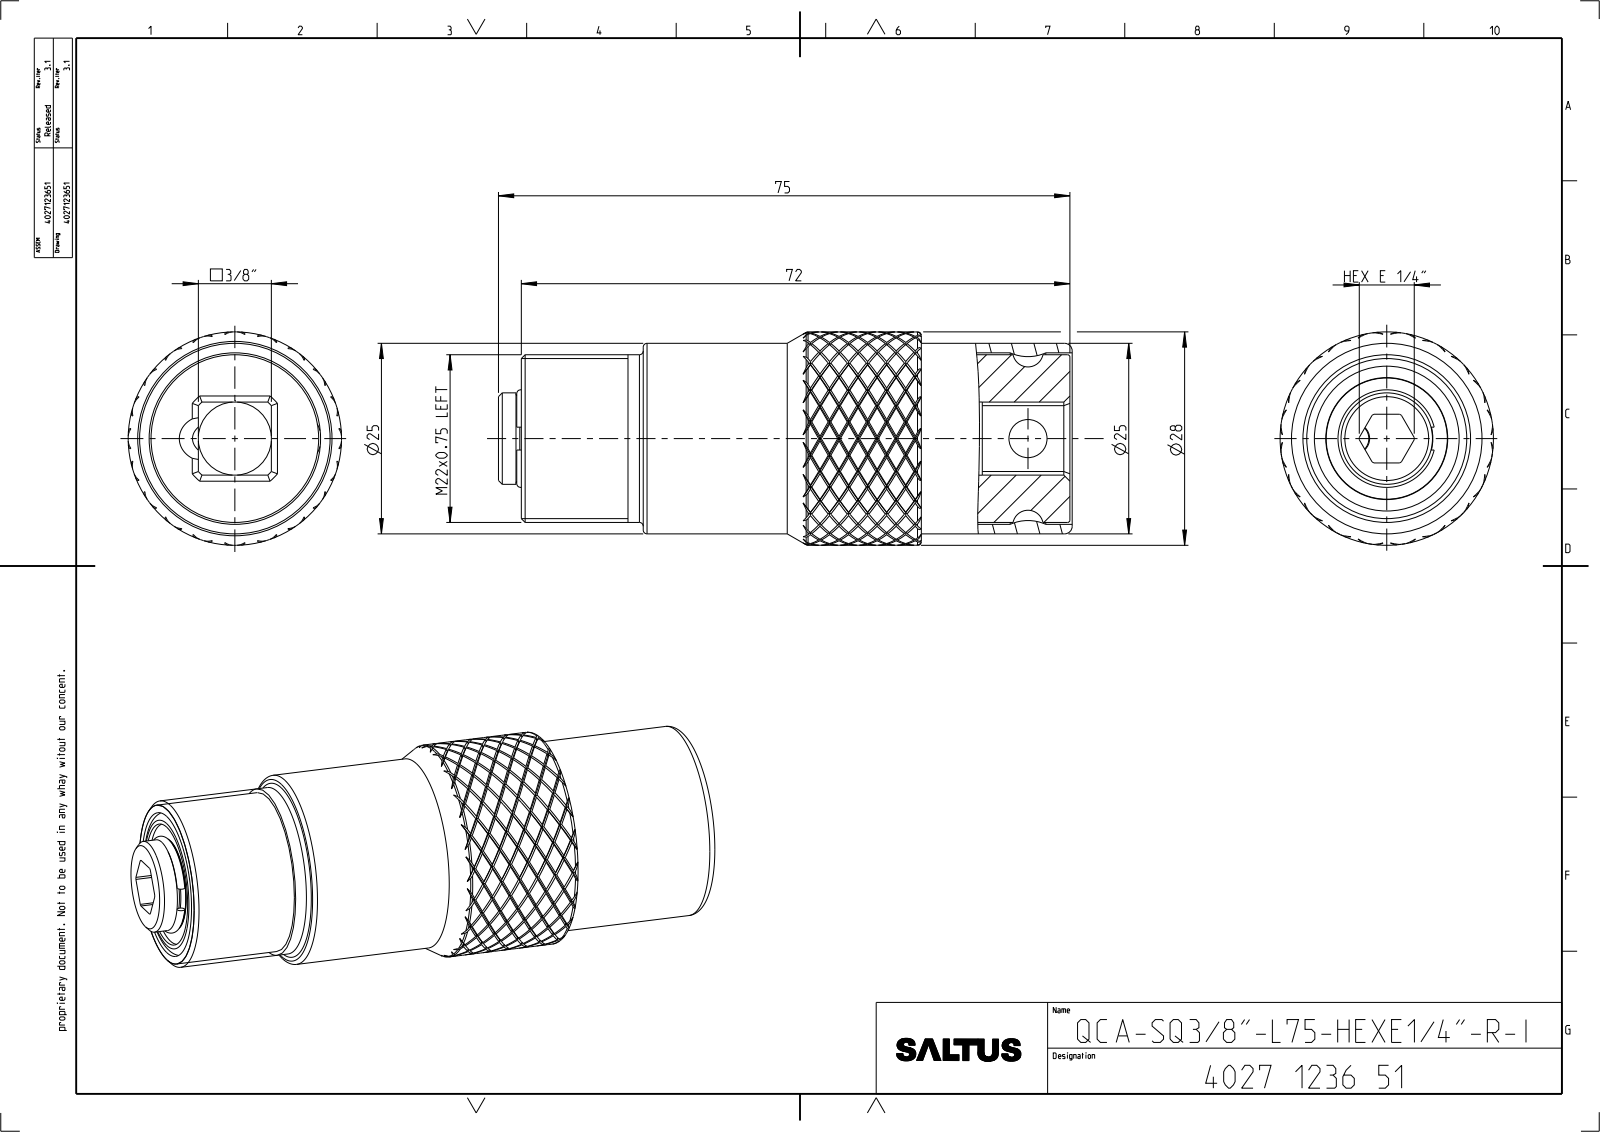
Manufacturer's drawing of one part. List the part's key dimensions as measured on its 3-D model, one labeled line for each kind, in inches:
Part name (STEP PRODUCT): 4027123651_ASM
STEP written by: CREO PARAMETRIC BY PTC INC, 2022414 (CONFIG_CONTROL_DESIGN)
Units: inches
Bodies: 0 solids, 1526 faces (48 planar, 342 cylindrical, 1136 other)
Overall size (bounding box): 2.965 × 1.102 × 1.102
Round holes (diameter × count): ⌀0.079 ×2, ⌀0.165 ×1, ⌀0.197 ×1, ⌀0.295 ×1, ⌀0.378 ×1, ⌀0.63 ×1, ⌀0.886 ×1, ⌀1.004 ×1
Round bosses / shafts (diameter × count): ⌀1.102 ×1, ⌀0.984 ×1, ⌀0.866 ×1, ⌀0.472 ×1, ⌀0.425 ×1
Partial cylindrical surfaces — rounded edges, fillets, slot ends (radius × count): R0.079 ×6, R0.118 ×1, R0.142 ×1, R0.254 ×1, R0.256 ×1
Main face-to-face distances: 0.63, 1.98, 0.251, 0.827, 0.377, 0.063, 0.314, 0.5, 1.48, 0.126
Hole centre spacings: 0.522, 0.64, 1.004, 1.526, 1.644, 2.165
